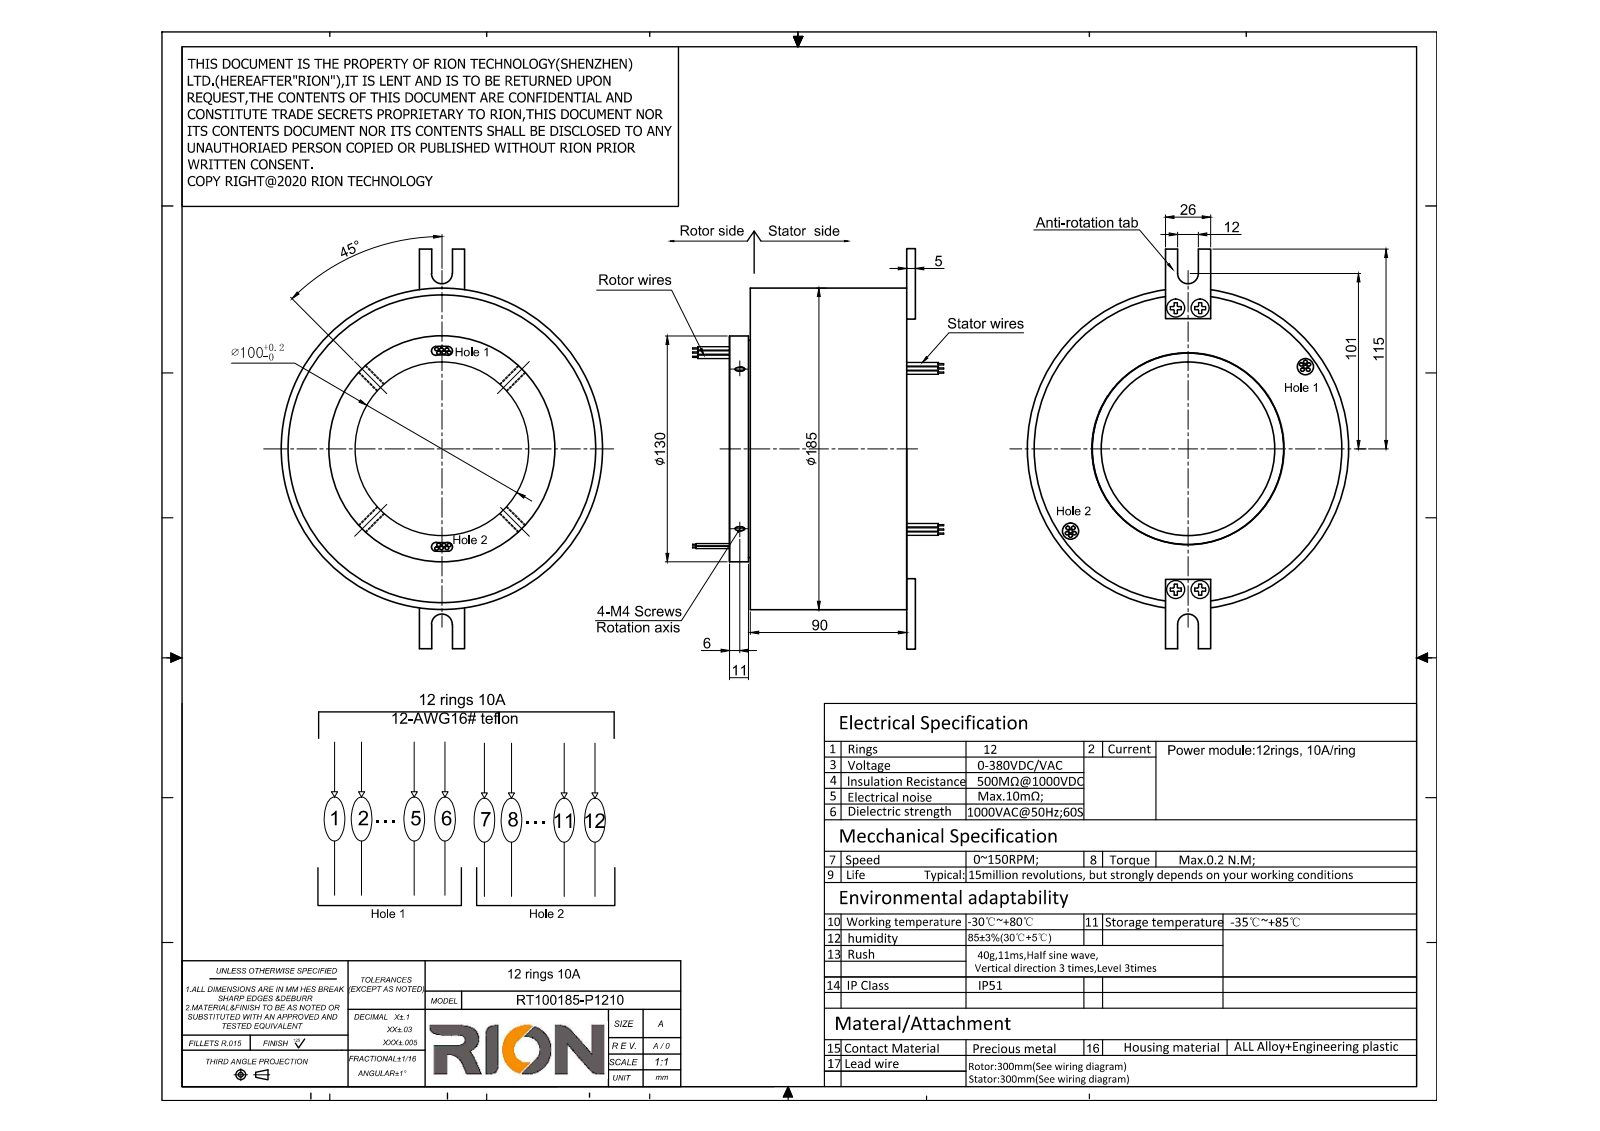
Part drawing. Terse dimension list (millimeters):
name: RT100185-P1210-VC
written by: SolidWorks 2014 (CONFIG_CONTROL_DESIGN)
unit: mm
bodies: 1 solid, 166 faces (54 planar, 84 cylindrical, 28 other)
size: 230 × 185 × 140
volume: 1 782 000 mm³; area: 139 060 mm²
holes: 4× ⌀5, 4× ⌀5.5, 2× ⌀8, 1× ⌀100
bosses: 24× ⌀2.1, 1× ⌀185, 1× ⌀130, 1× ⌀120
rounds: 4× R2.5, 2× R6
face distances: 90, 12, 102, 1, 11, 91, 5, 95, 96, 107
hole spacings: 81.3, 14, 69.31, 81.83, 82.5, 141.9, 148.42, 162
